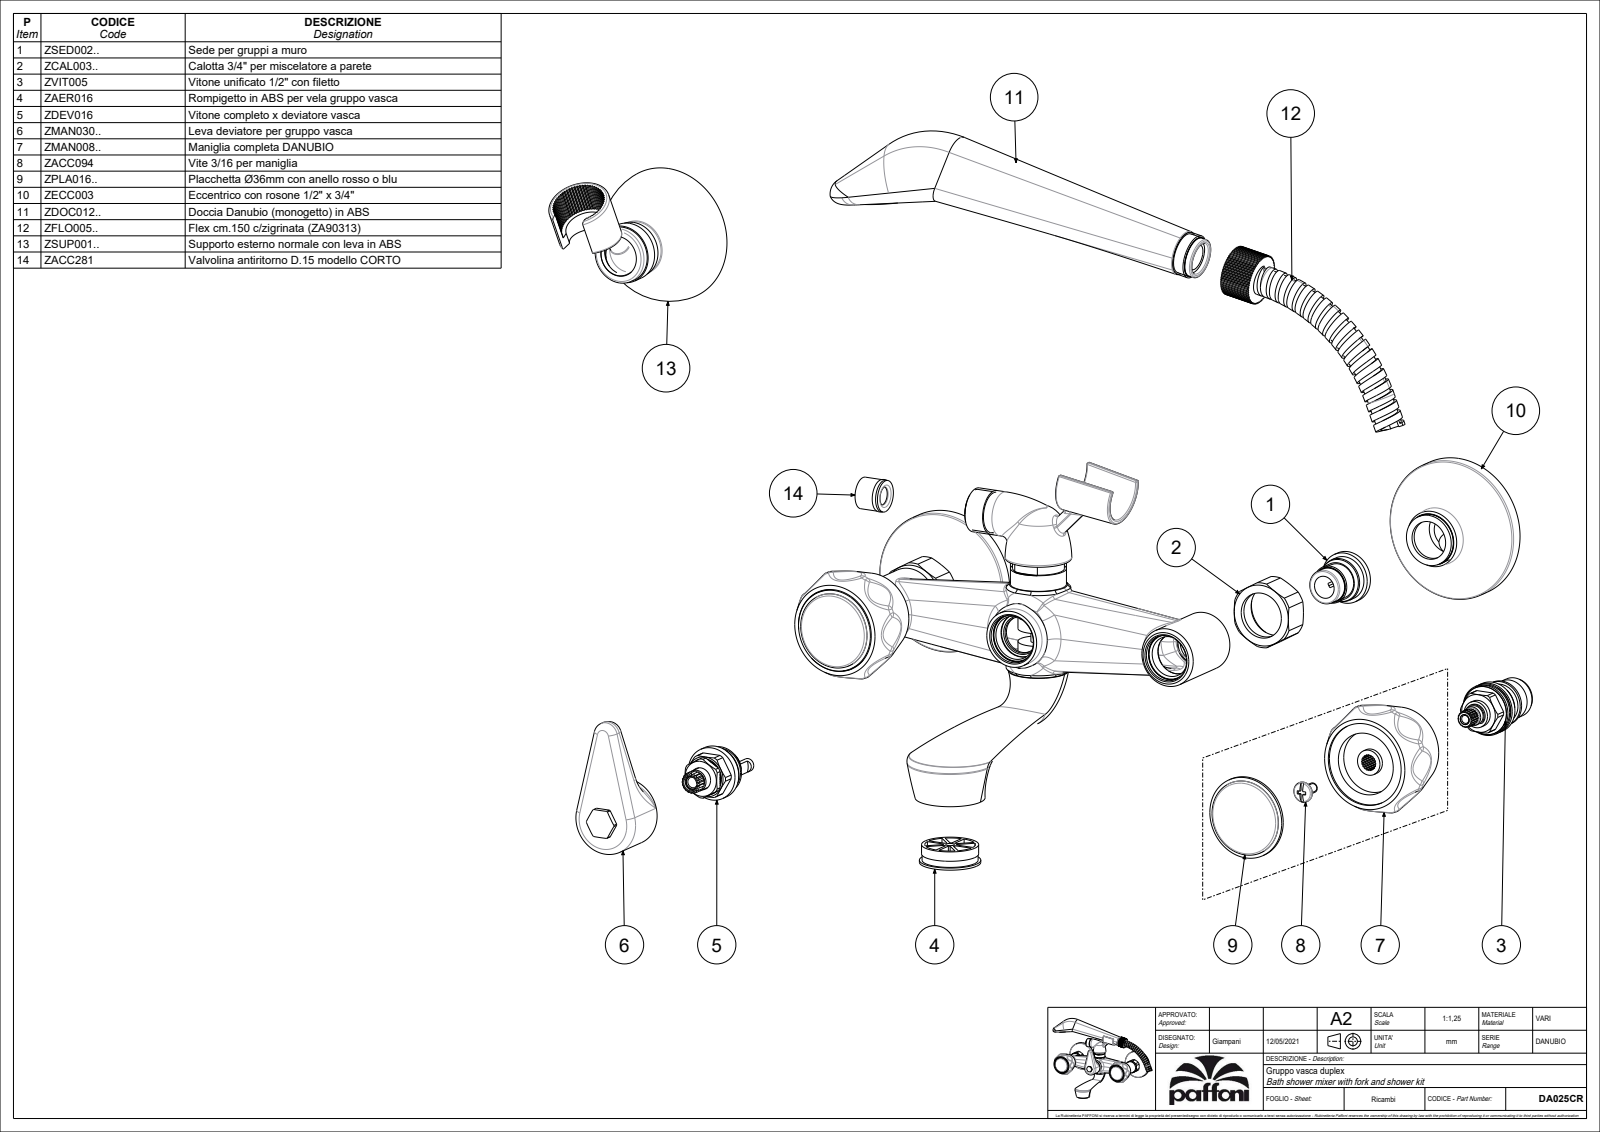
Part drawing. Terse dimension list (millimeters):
name: DA025CR
written by: CREO PARAMETRIC BY PTC INC, 2020044 (CONFIG_CONTROL_DESIGN)
unit: mm
bodies: 5 solids, 1839 faces (608 planar, 448 cylindrical, 783 other)
size: 446.55 × 250.66 × 155
volume: 359 335 mm³; area: 191 301 mm²
holes: 3× ⌀10.5, 3× ⌀18, 3× ⌀25, 2× ⌀21.5, 2× ⌀23.5, 2× ⌀24.1, 2× ⌀26.7, 2× ⌀35.8, 2× ⌀39, 2× ⌀65.4, 1× ⌀4, 1× ⌀6
bosses: 4× ⌀20.5, 2× ⌀66, 2× ⌀38.5, 2× ⌀30.5, 2× ⌀27.5, 2× ⌀26, 2× ⌀25.6, 2× ⌀24
rounds: 28× R1, 16× R21.31, 5× R3, 4× R3.5, 3× R6, 3× R10, 3× R15.5, 2× R0.5
face distances: 29, 6, 50, 9.5, 6.6, 79, 6.7, 0.5, 30.5, 1.5
hole spacings: 79, 82, 158, 227.47, 291.55, 361.58
